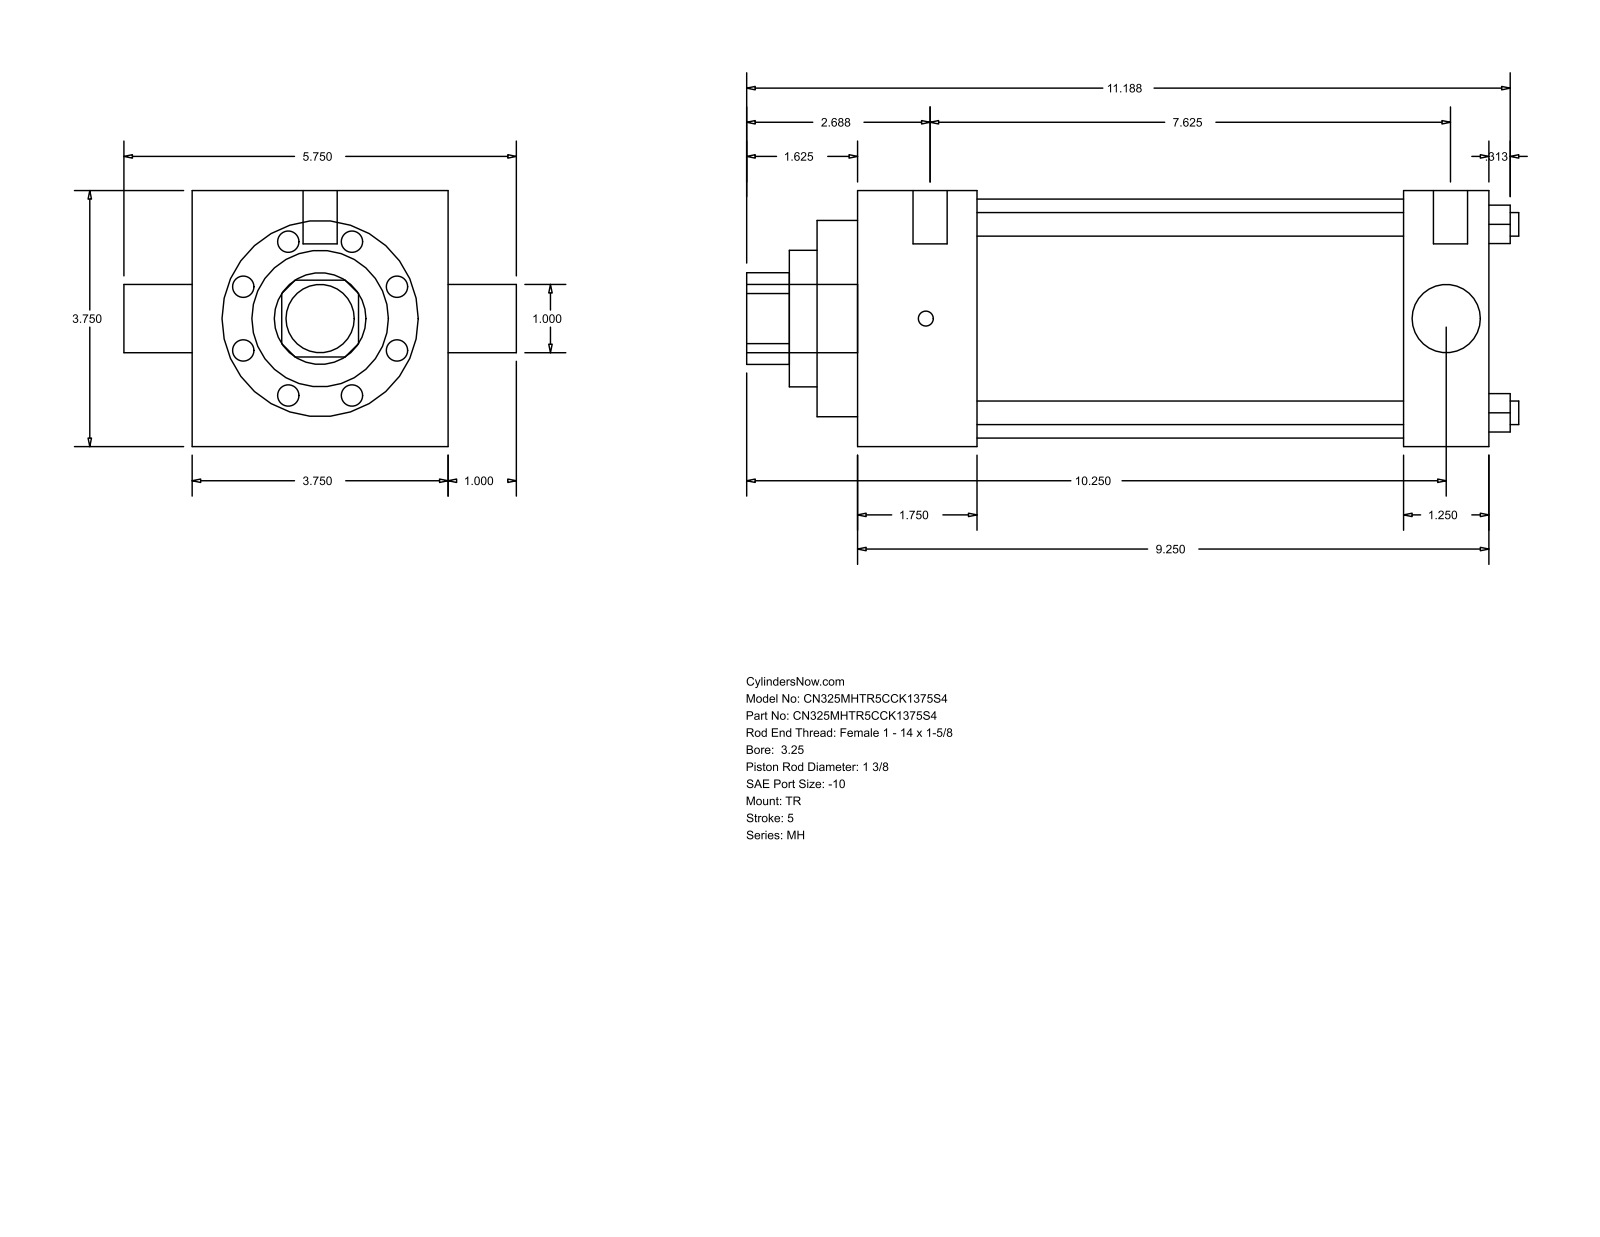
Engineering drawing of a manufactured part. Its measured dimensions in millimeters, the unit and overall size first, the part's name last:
Units: millimetres
Overall size (bounding box): 287.34 × 146.05 × 95.25
Round holes (diameter × count): ⌀8.76 ×4, ⌀25.4 ×1, ⌀34.92 ×1, ⌀50.8 ×1, ⌀73.03 ×1, ⌀88.9 ×1
Round bosses / shafts (diameter × count): ⌀5.56 ×3, ⌀12.7 ×2, ⌀25.4 ×1
Partial cylindrical surfaces — rounded edges, fillets, slot ends (radius × count): R17.06 ×1
Main face-to-face distances: 95.24, 234.96, 44.45, 203.2, 158.75, 190.51, 31.76, 15.08, 59.53, 218.28
Hole centre spacings: 49.57, 70.1, 99.14
Bodies: 0 solids, 86 faces (61 planar, 25 cylindrical, 0 other)
Part name (STEP PRODUCT): MH_TR__0325_1.375
STEP written by: GSSL Pune (CONFIG_CONTROL_DESIGN)
